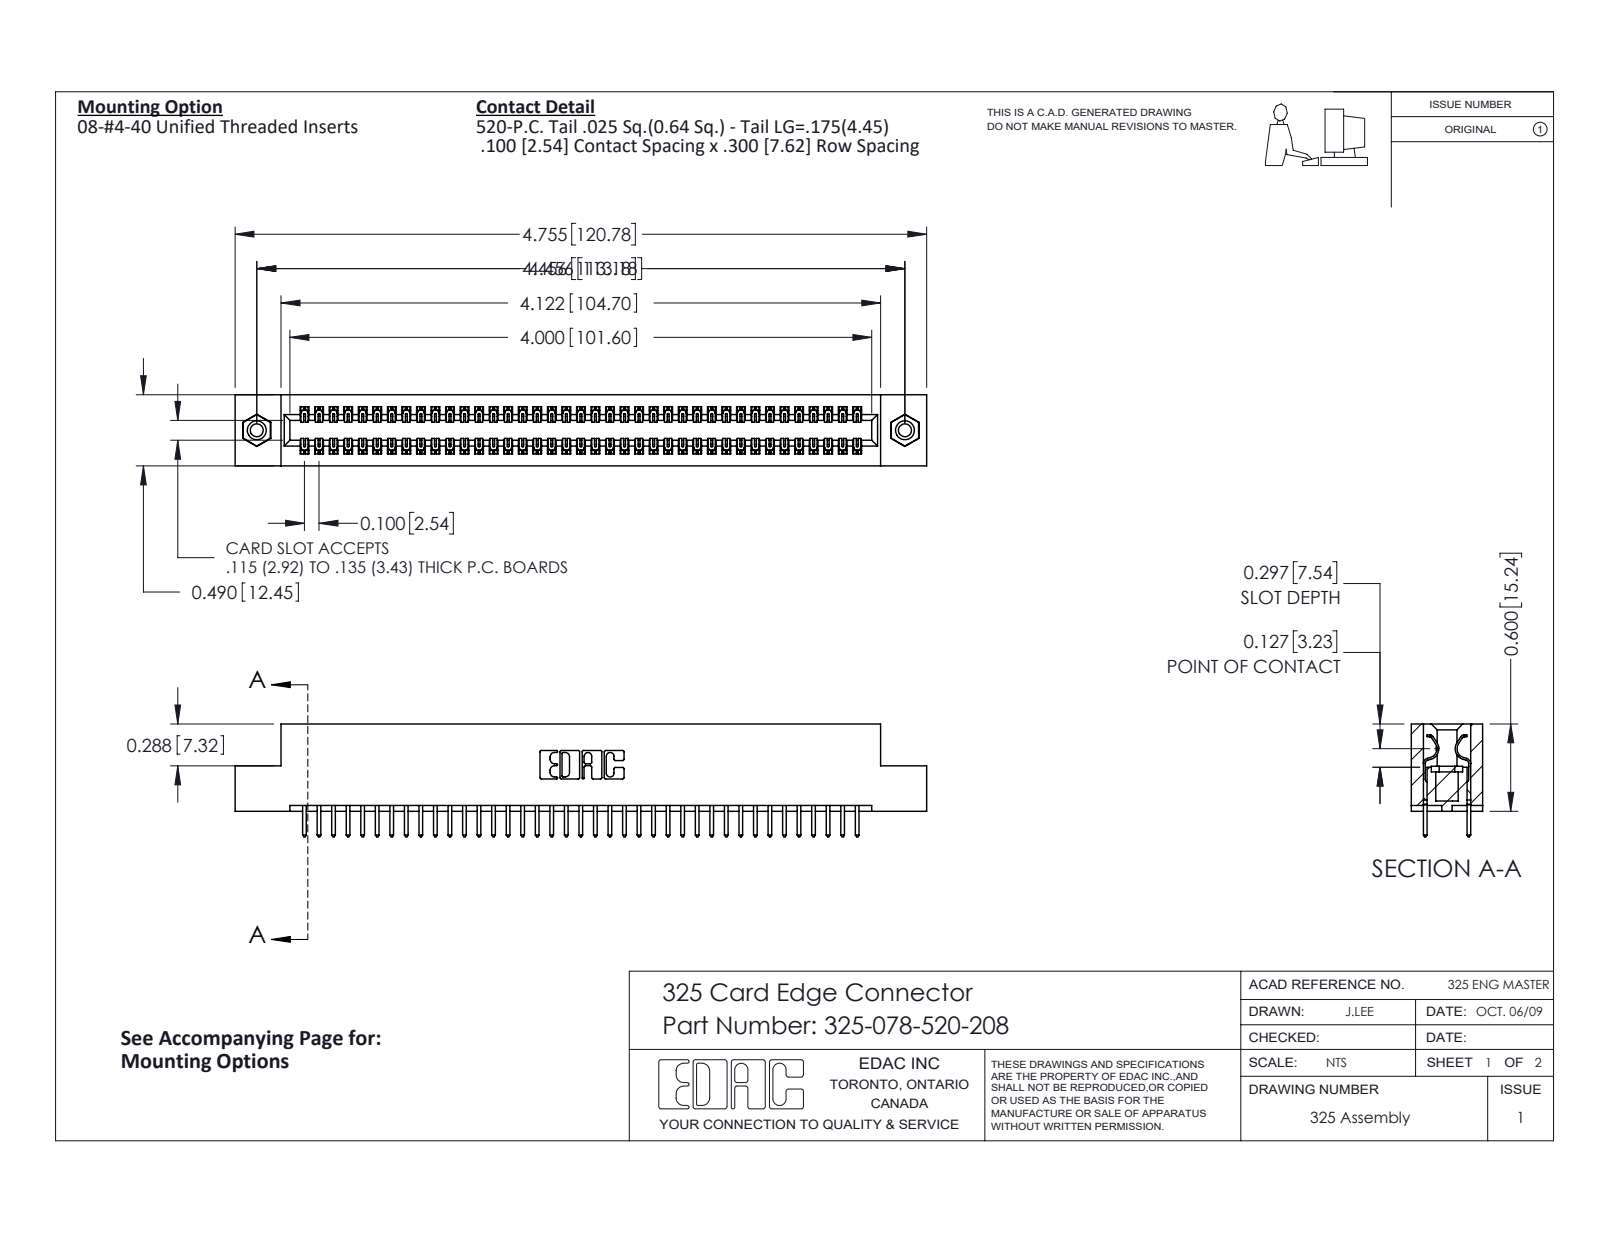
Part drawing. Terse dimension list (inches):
name: 325 Part_TI; 325-078-520-208; 325-292-001_325-293-120; 345-250-001_345-250-003-102
written by: SolidWorks 2016 (CONFIG_CONTROL_DESIGN)
unit: in
bodies: 81 solids, 4230 faces (2910 planar, 1304 cylindrical, 16 other)
size: 4.755 × 0.775 × 0.49
volume: 0.949 in³; area: 28.83 in²
holes: 2× ⌀0.089, 2× ⌀0.125, 2× ⌀0.16
bosses: 2× ⌀0.155
rounds: 117× R0.006, 78× R0.01, 22× R0.01, 6× R0.007, 6× R0.031, 3× R0.026, 2× R0.014, 2× R0.022
face distances: 0.083, 0.407, 0.49, 0.3, 0.107, 0.383, 0.025, 0.325, 0.275, 0.56
hole spacings: 4.456
